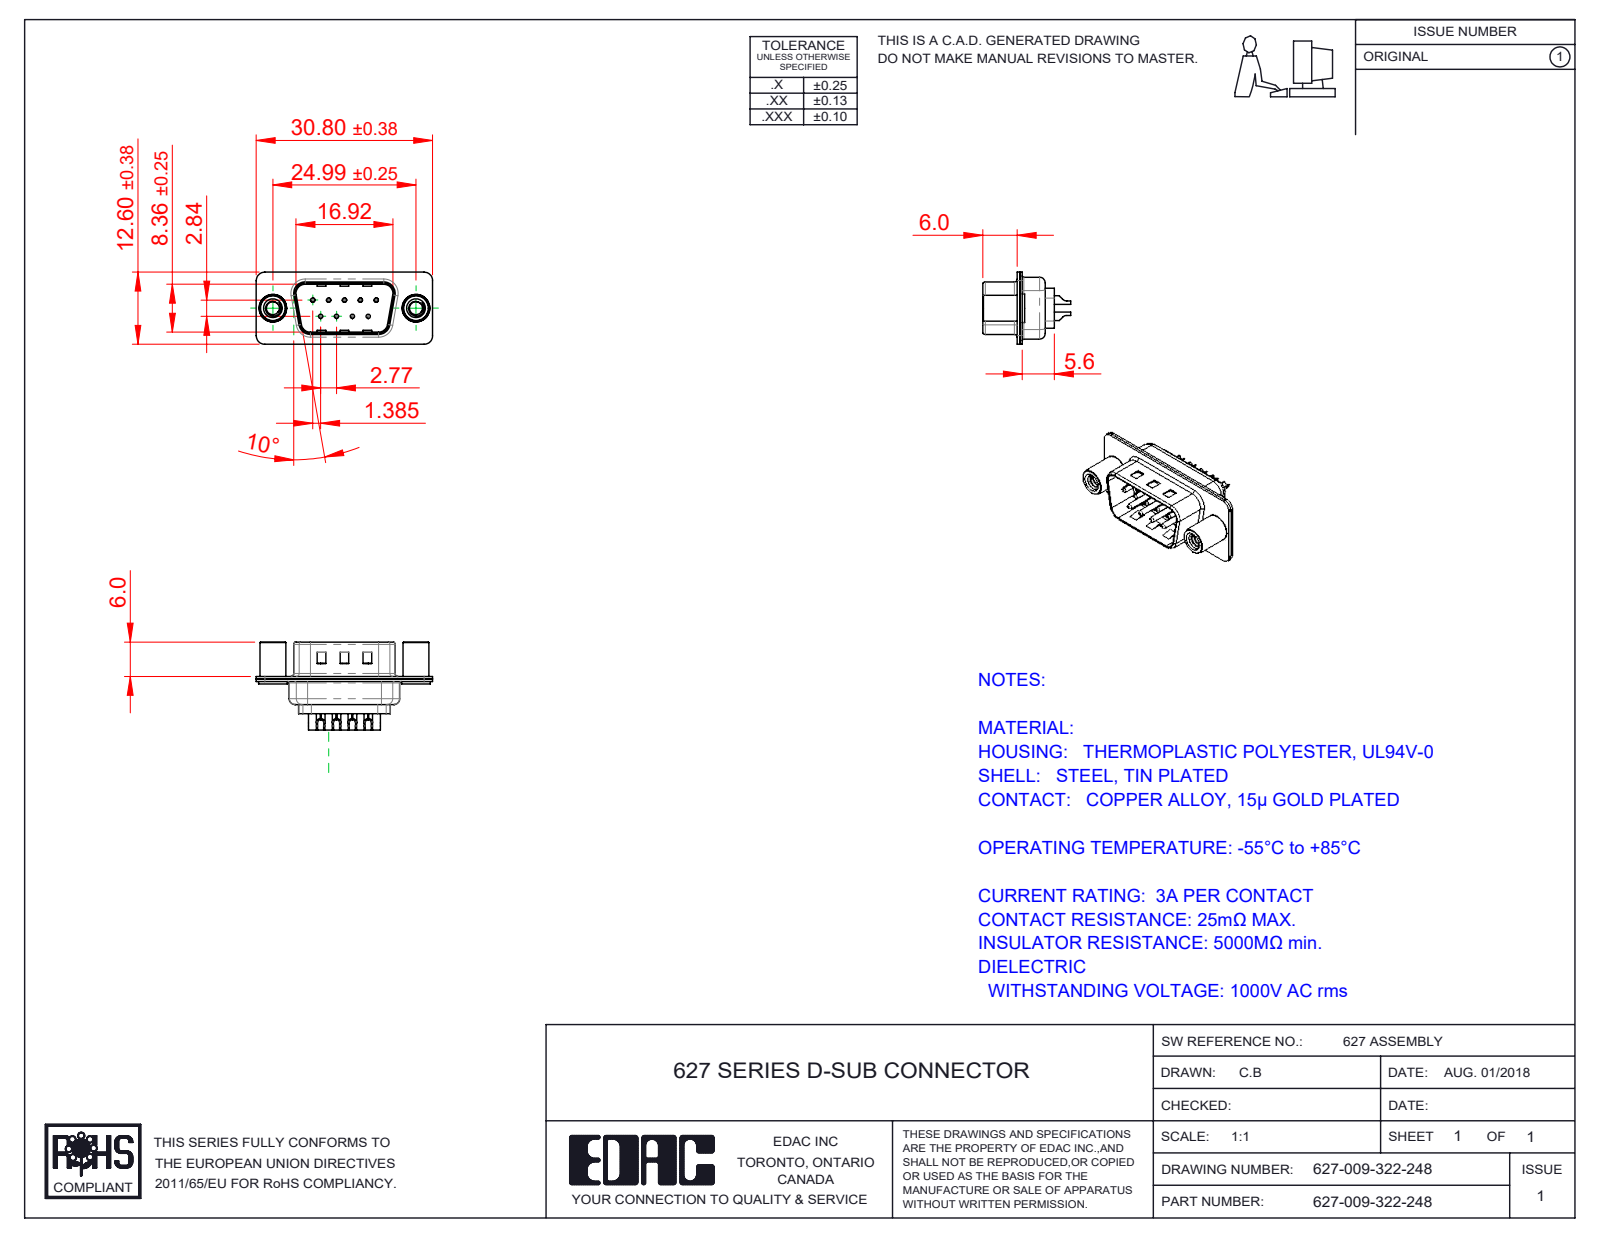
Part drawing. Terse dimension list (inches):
name: 627 4-40 Threaded Standoff; 627 Contact Row 1_22L; 627 Shell Rear_09 Contacts; 627 Shell Front_09 Contacts (+3 more)
written by: SolidWorks 2020 (CONFIG_CONTROL_DESIGN)
unit: in
bodies: 14 solids, 914 faces (235 planar, 418 cylindrical, 261 other)
size: 1.213 × 0.604 × 0.496
volume: 0.084 in³; area: 6.428 in²
holes: 9× ⌀0.014, 9× ⌀0.043, 9× ⌀0.063, 2× ⌀0.089, 2× ⌀0.157, 2× ⌀0.189
bosses: 9× ⌀0.079, 9× ⌀0.059, 9× ⌀0.03, 2× ⌀0.197, 2× ⌀0.193, 2× ⌀0.177
rounds: 18× R0.059, 12× R0.079, 8× R0.02, 8× R0.063, 6× R0.039, 4× R0.01, 4× R0.024, 4× R0.026
face distances: 0.016, 0.018, 0.035, 0.032, 0.377, 0.055, 0.345, 0.02, 0.059, 0.256
hole spacings: 0.124, 0.109, 0.218, 0.198, 0.198, 0.327, 0.294, 0.295
